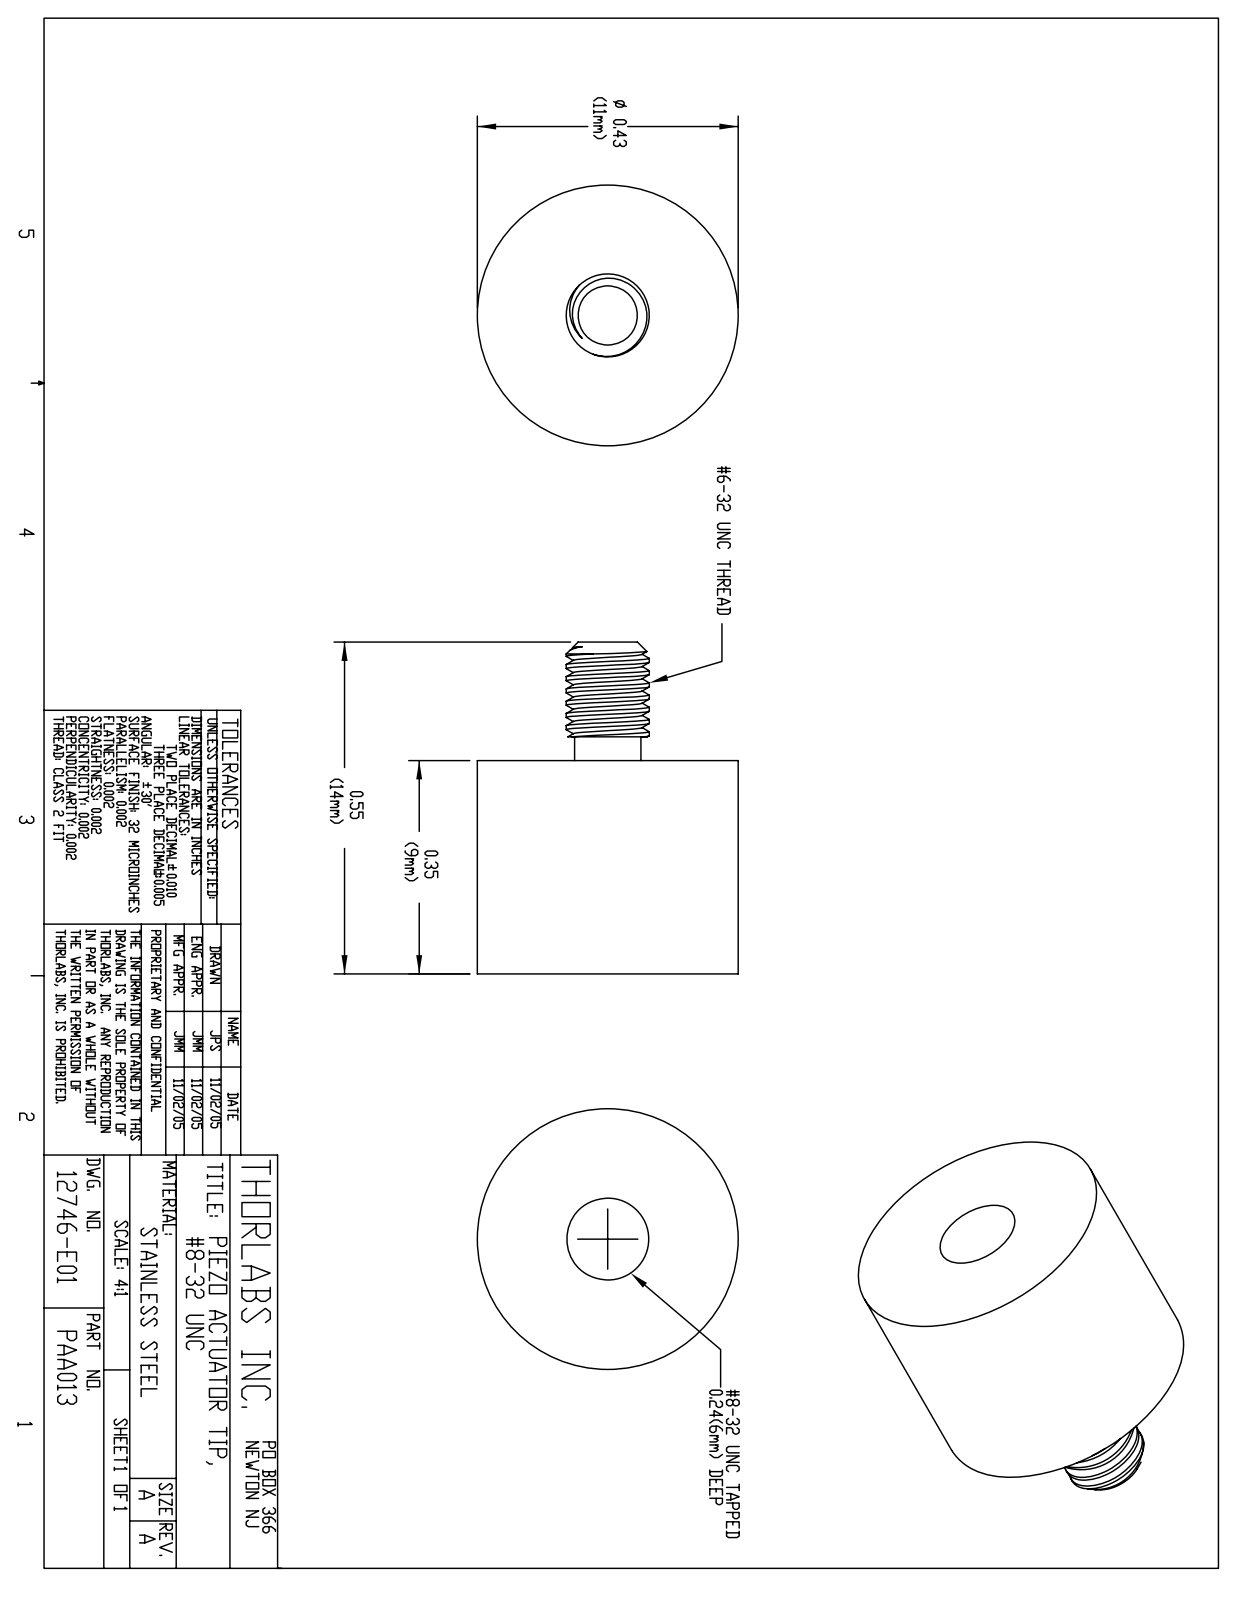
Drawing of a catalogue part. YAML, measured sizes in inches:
part_name: "12746-E0W"
step_written_by: "SolidWorks 2007 (AUTOMOTIVE_DESIGN)"
units: inches
bodies: {solids: 0, faces: 28, planar: 3, cylindrical: 21, other: 4}
overall_size: [0.551, 0.433, 0.433]
round_holes:
  - {diameter: 0.136, count: 1}
round_bosses_or_shafts:
  - {diameter: 0.433, count: 1}
  - {diameter: 0.138, count: 1}
  - {diameter: 0.11, count: 1}
face_to_face_distances: [0.354, 0.551, 0.197]
